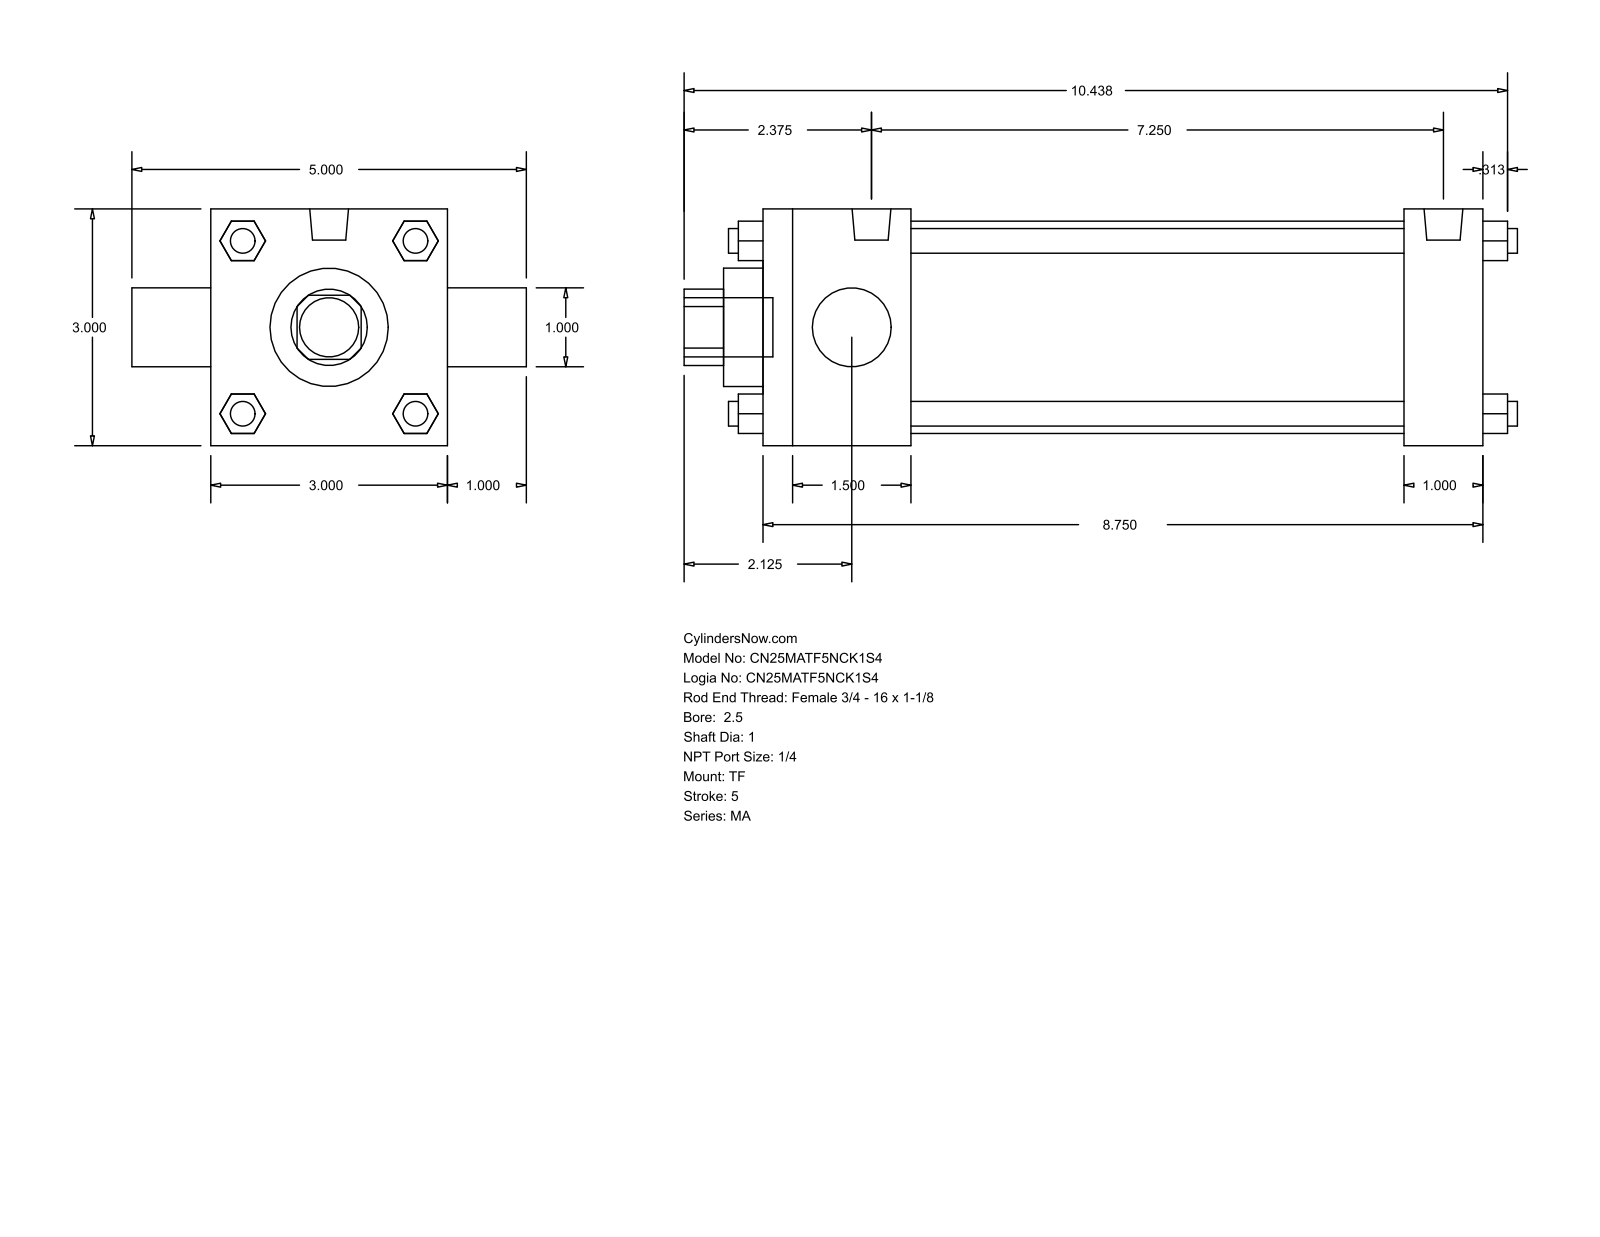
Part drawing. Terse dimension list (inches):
name: MA_TF__0250_1
written by: GSSL Pune (CONFIG_CONTROL_DESIGN)
unit: in
bodies: 0 solids, 120 faces (92 planar, 28 cylindrical, 0 other)
size: 10.563 × 5 × 3
holes: 2× ⌀1, 1× ⌀1.5, 1× ⌀2.69
bosses: 7× ⌀0.313, 2× ⌀0.492, 1× ⌀0.75
rounds: 1× R0.484
face distances: 3, 9.125, 1, 0.5, 1.875, 8.125, 6.25, 7.25, 4, 1.095
